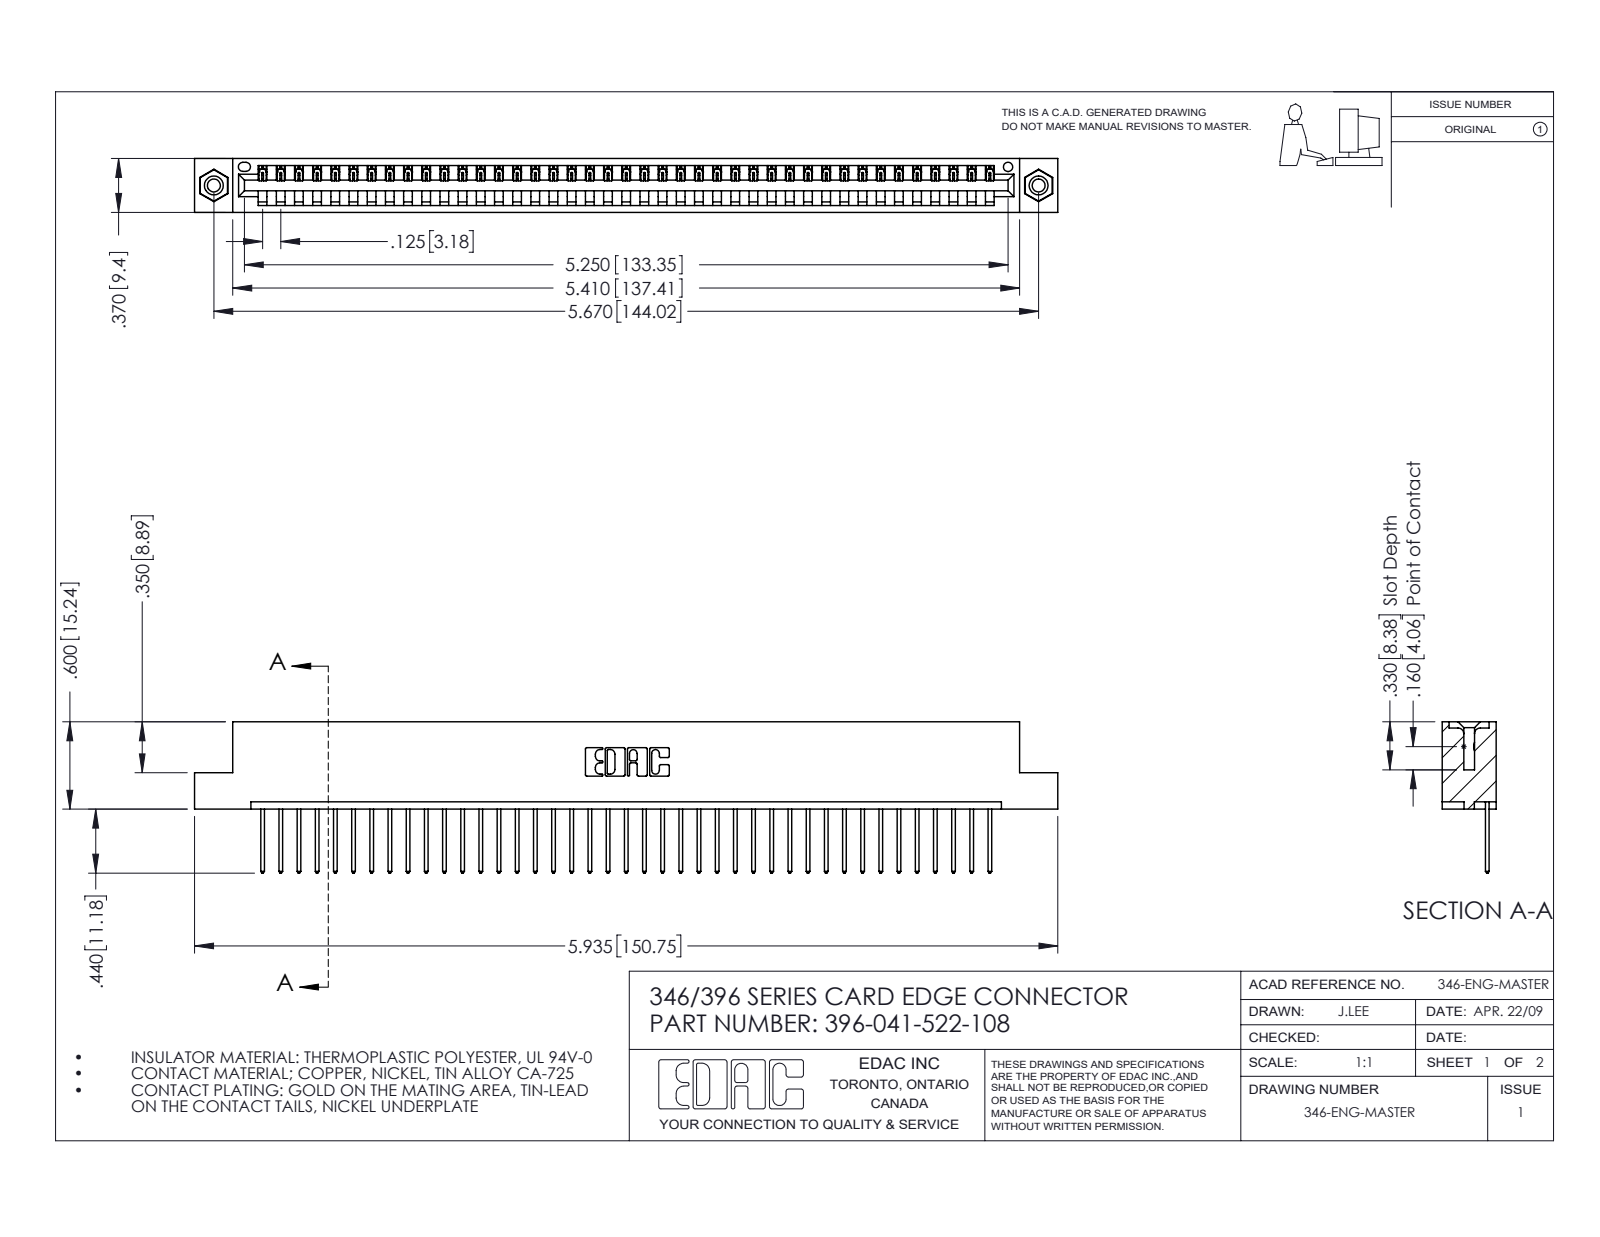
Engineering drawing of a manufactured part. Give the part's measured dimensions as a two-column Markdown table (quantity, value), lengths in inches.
| quantity | value |
| --- | --- |
| part name | 345-292-001_345-293-122; 396-041-522-108; 346 Part_Flush Mounting Lugs - 0.156 Dia-TI; 345-250-001_345-250-003-102 |
| STEP written by | SolidWorks 2016 (CONFIG_CONTROL_DESIGN) |
| units | inches |
| bodies | 44 solids, 2560 faces (1748 planar, 796 cylindrical, 16 other) |
| overall size | 5.935 × 1.04 × 0.37 |
| volume | 0.88 in³ |
| surface area | 28.19 in² |
| round holes (diameter × count) | 0.089 × 2, 0.125 × 2, 0.156 × 2, 0.064 × 1 |
| round bosses / shafts (diameter × count) | 0.155 × 2 |
| partial cylindrical surfaces (radius × count) | 0.006 × 82, 0.01 × 82, 0.01 × 22, 0.007 × 6, 0.031 × 6, 0.026 × 3, 0.031 × 2, 0.04 × 2 |
| main face-to-face distances | 0.048, 0.322, 0.37, 0.25, 0.072, 0.298, 0.025, 0.148, 0.222, 0.1 |
| hole center spacings | 0.246, 5.461, 5.67 |
